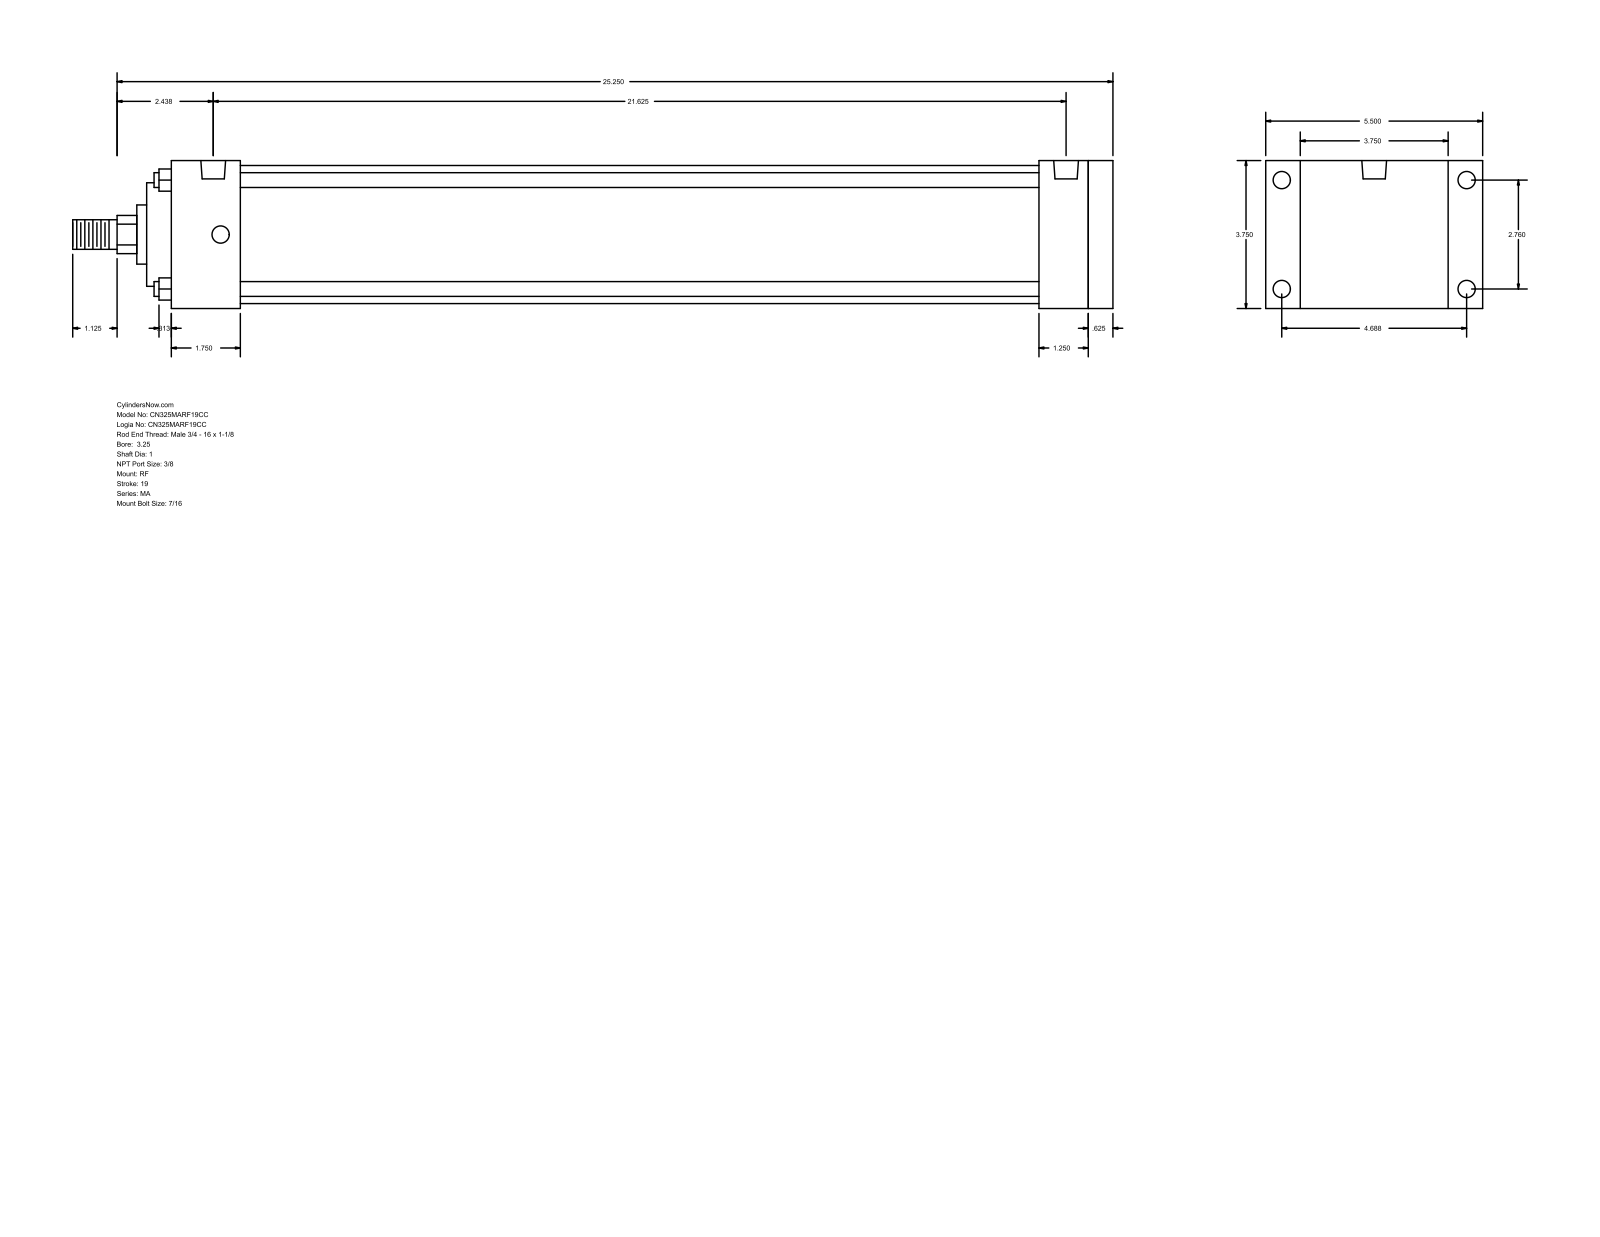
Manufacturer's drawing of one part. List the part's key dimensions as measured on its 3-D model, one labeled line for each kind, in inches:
Part name (STEP PRODUCT): MA_RF__0325_1
STEP written by: GSSL Pune (CONFIG_CONTROL_DESIGN)
Units: inches
Bodies: 0 solids, 94 faces (65 planar, 29 cylindrical, 0 other)
Overall size (bounding box): 26.375 × 5.5 × 3.75
Round holes (diameter × count): ⌀0.437 ×8, ⌀0.627 ×2
Round bosses / shafts (diameter × count): ⌀0.375 ×4, ⌀3.5 ×1, ⌀2.625 ×1, ⌀1.5 ×1, ⌀1 ×1, ⌀0.75 ×1
Partial cylindrical surfaces — rounded edges, fillets, slot ends (radius × count): R0.484 ×1
Main face-to-face distances: 3.75, 23.875, 0.625, 23.25, 0.875, 4.625, 1.875, 24.5, 22, 1.25
Hole centre spacings: 2.76, 4.687, 5.439, 21.25, 0.187, 0.188, 21.437, 21.438
